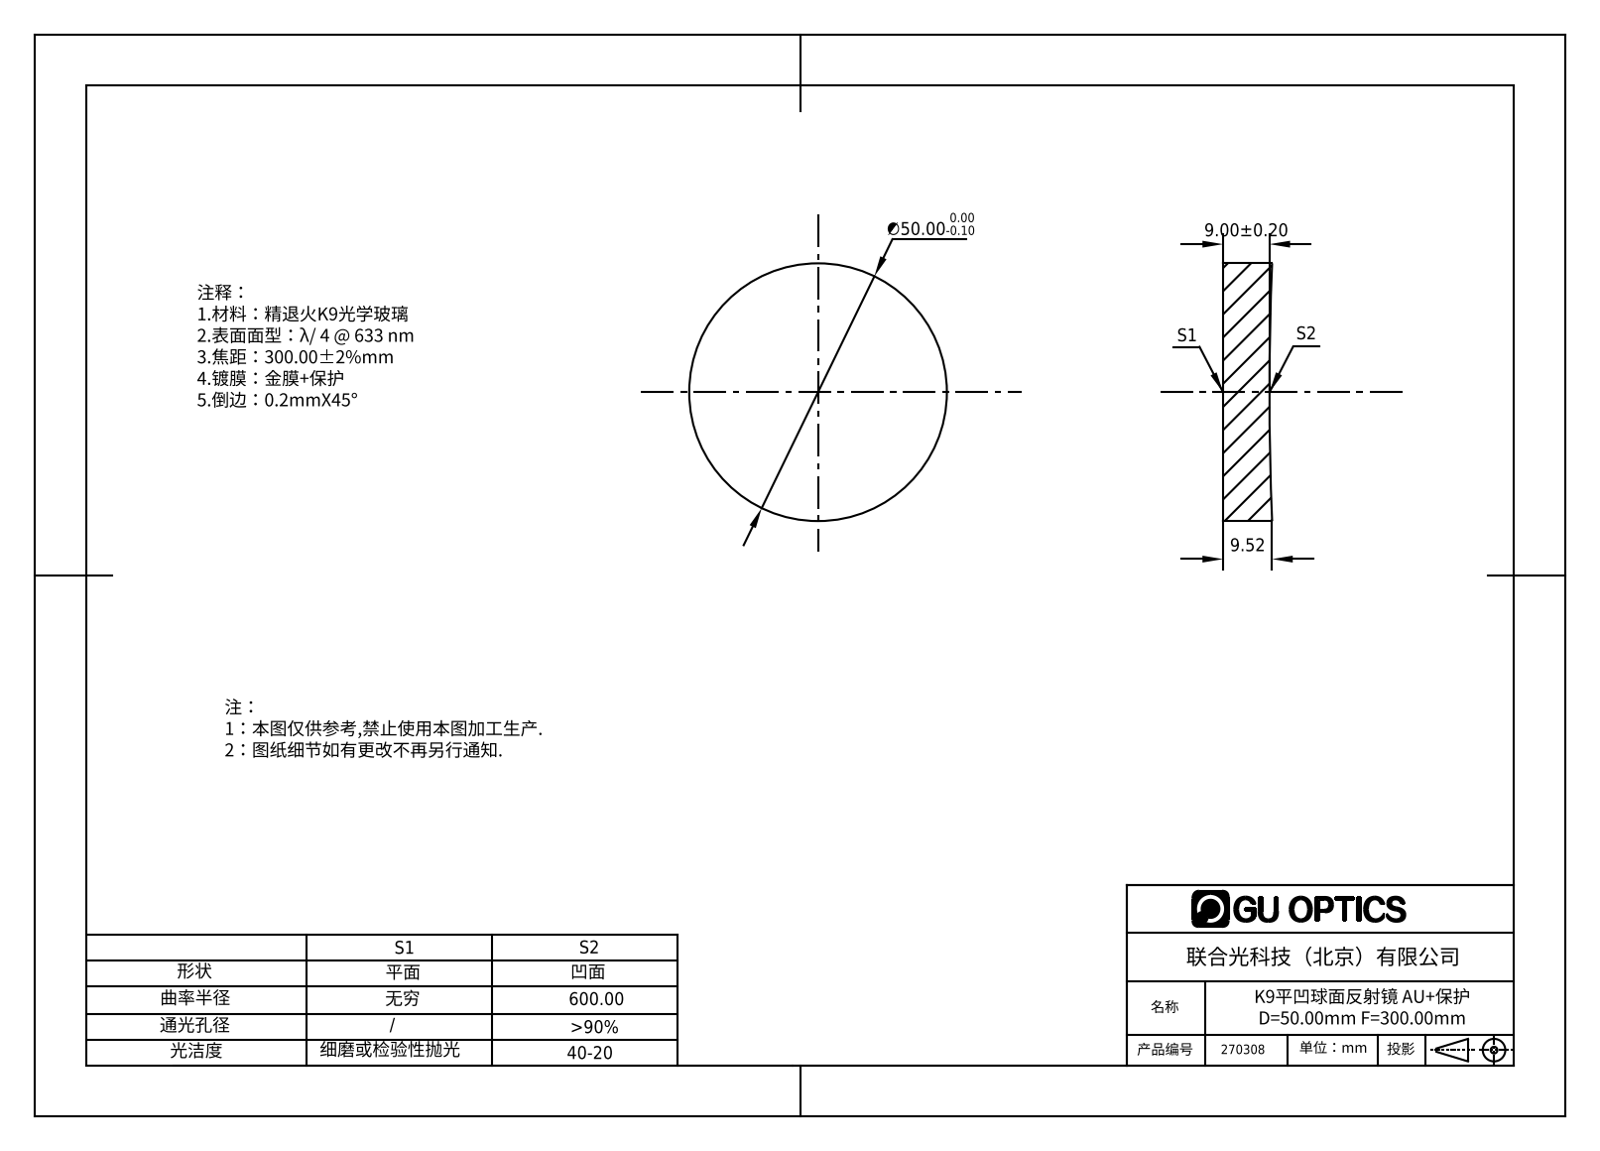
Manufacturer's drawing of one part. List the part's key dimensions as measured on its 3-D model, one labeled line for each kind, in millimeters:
Part name (STEP PRODUCT): 270048
STEP written by: SolidWorks 2016 (AUTOMOTIVE_DESIGN)
Units: millimetres
Bodies: 1 solid, 5 faces (1 planar, 2 cylindrical, 2 other)
Overall size (bounding box): 50 × 50 × 9.52
Volume: 18 183 mm³ · Surface area: 5 423 mm²
Round bosses / shafts (diameter × count): ⌀50 ×1
